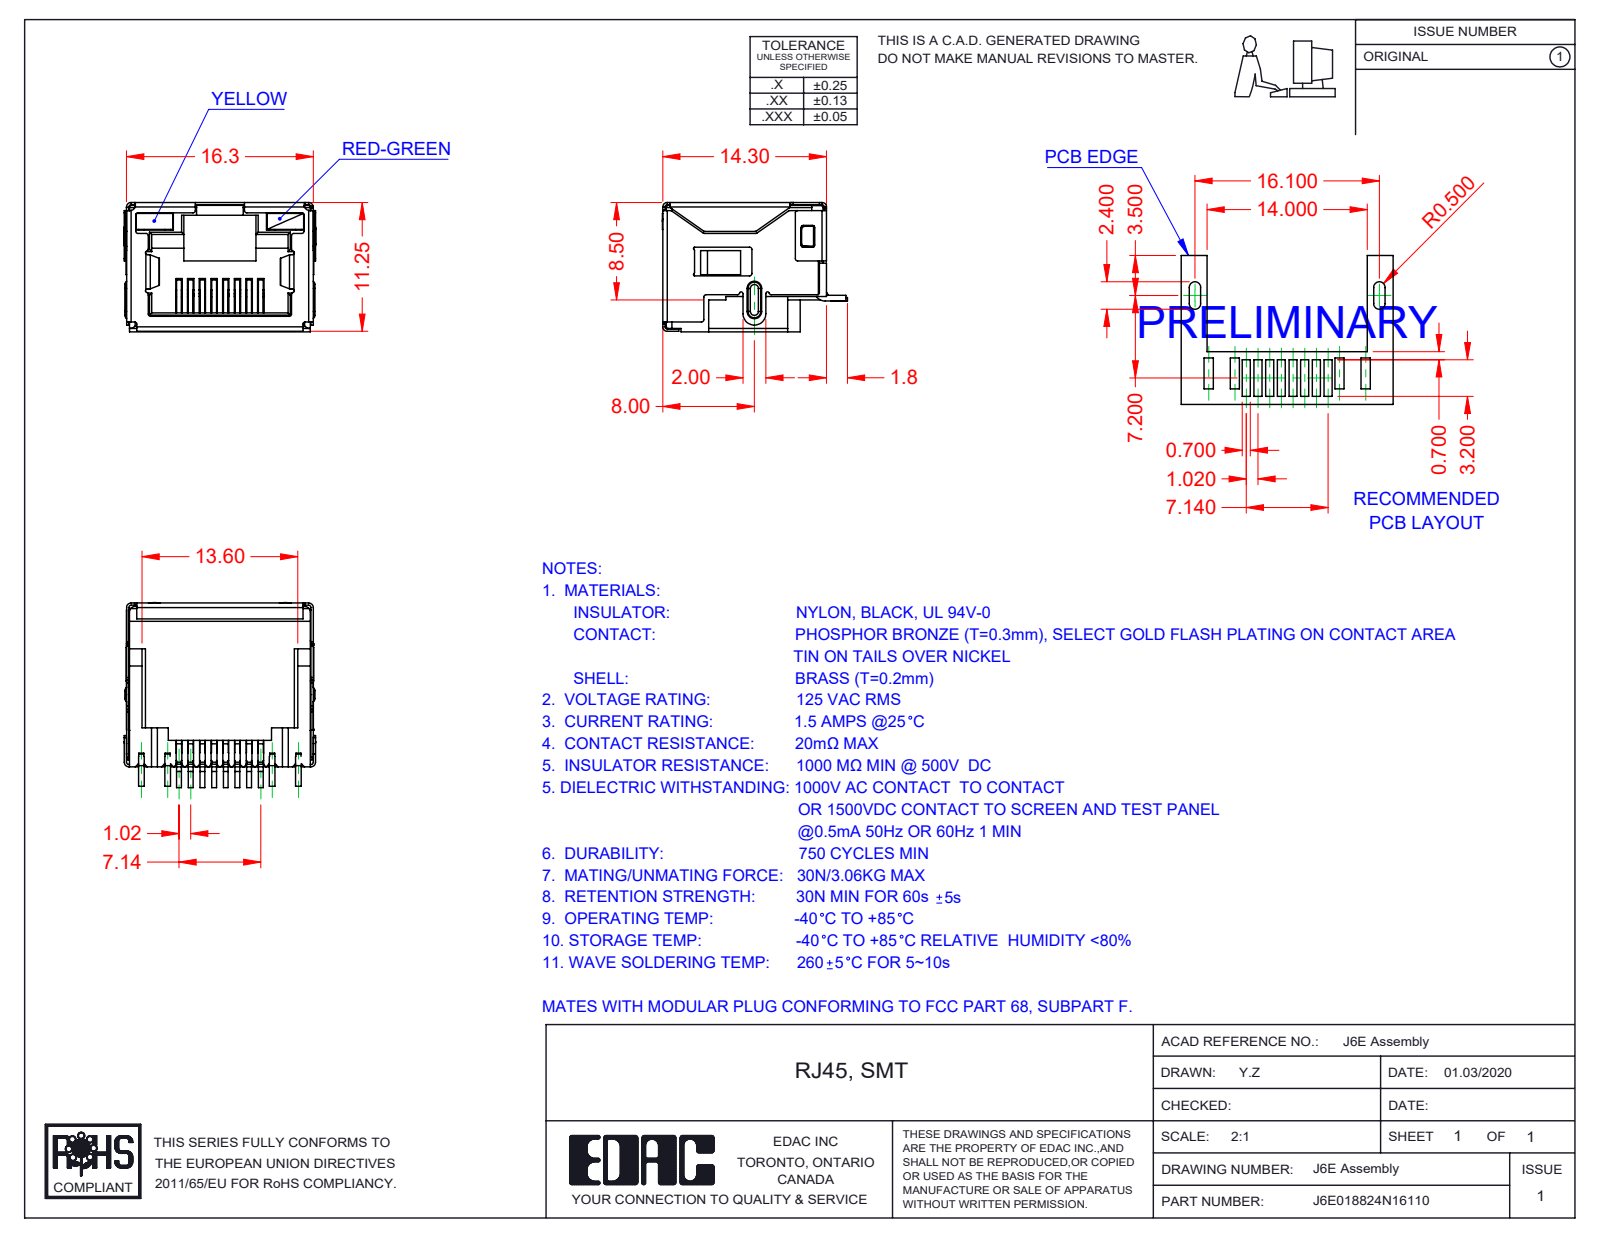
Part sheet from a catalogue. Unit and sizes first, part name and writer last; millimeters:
Units: millimetres
Overall size (bounding box): 16.75 × 16.15 × 11.3
Partial cylindrical surfaces — rounded edges, fillets, slot ends (radius × count): R0.2 ×82, R0.25 ×17, R0.4 ×13, R0.5 ×13, R0.1 ×10, R0.15 ×7, R0.3 ×4, R1 ×3
Main face-to-face distances: 11.05, 16.05, 16.1, 15.85, 11.1, 11.3, 2.4, 0.7, 9.85, 0.49
Volume: 1 109 mm³ · Surface area: 4 045 mm²
Bodies: 12 solids, 1498 faces (1099 planar, 349 cylindrical, 50 other)
Part name (STEP PRODUCT): 6E Contacts; 6E Shield_LED; 6E Insulator_LED; J6E018824N16110 (+2 more)
STEP written by: SolidWorks 2016 (CONFIG_CONTROL_DESIGN)
